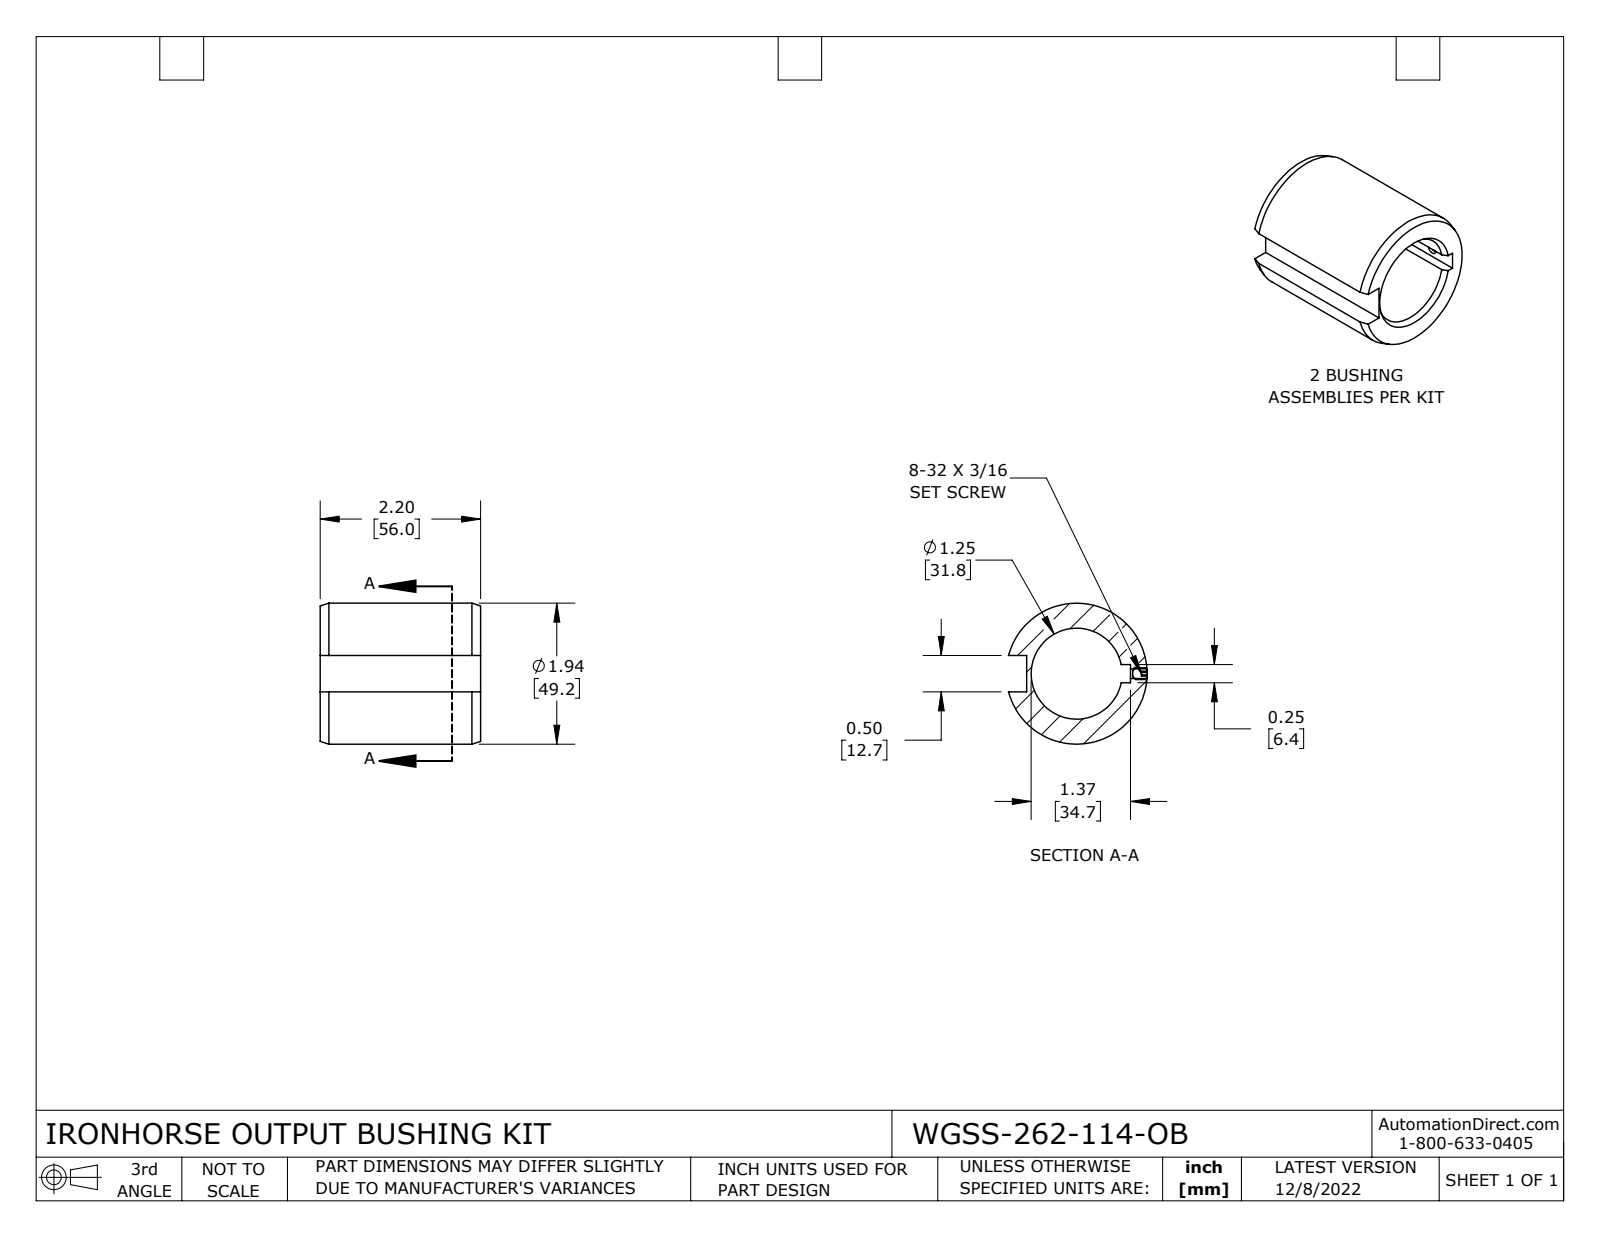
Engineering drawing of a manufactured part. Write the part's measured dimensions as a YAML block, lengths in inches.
part_name: "WGSS-262-114-OB"
step_written_by: "SolidWorks 2021 (CONFIG_CONTROL_DESIGN)"
units: inches
bodies: {solids: 2, faces: 40, planar: 17, cylindrical: 10, other: 13}
overall_size: [2.205, 1.937, 1.905]
volume: 3.389
surface_area: 26.41
round_holes:
  - {diameter: 0.136, count: 1}
  - {diameter: 1.25, count: 1}
round_bosses_or_shafts:
  - {diameter: 1.937, count: 1}
  - {diameter: 0.164, count: 1}
face_to_face_distances: [2.205, 0.125, 0.375, 0.5, 1.428, 0.25, 0.059, 0.03, 1.458, 0.197]
